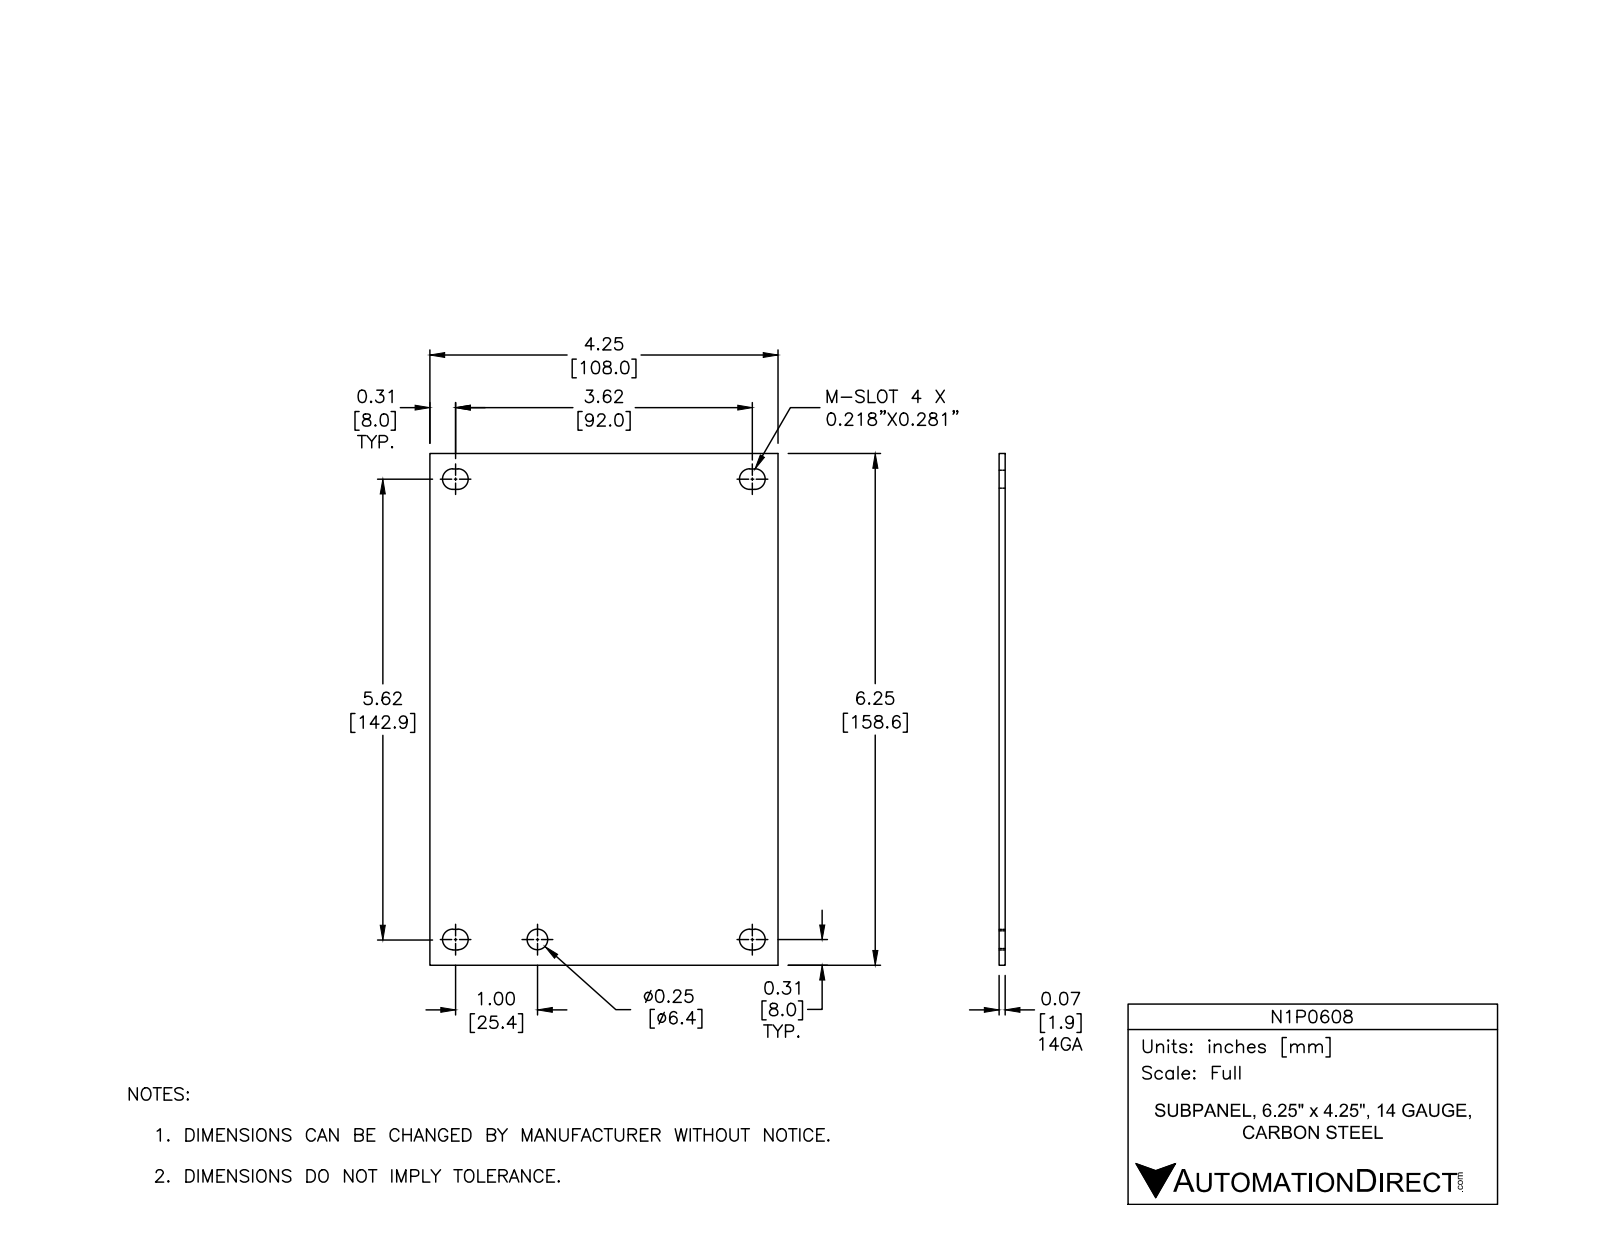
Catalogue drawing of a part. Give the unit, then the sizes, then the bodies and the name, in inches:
Units: inches
Overall size (bounding box): 6.25 × 4.25 × 0.074
Round holes (diameter × count): ⌀0.25 ×1
Partial cylindrical surfaces — rounded edges, fillets, slot ends (radius × count): R0.125 ×8
Main face-to-face distances: 0.074, 4.25, 6.25, 0.438, 5.812, 0.188, 6.062, 0.25, 5.624, 5.874
Volume: 1.943 in³ · Surface area: 54.39 in²
Bodies: 1 solid, 23 faces (14 planar, 9 cylindrical, 0 other)
Part name (STEP PRODUCT): N1P0608
STEP written by: Autodesk Inventor 2012 (AUTOMOTIVE_DESIGN)
